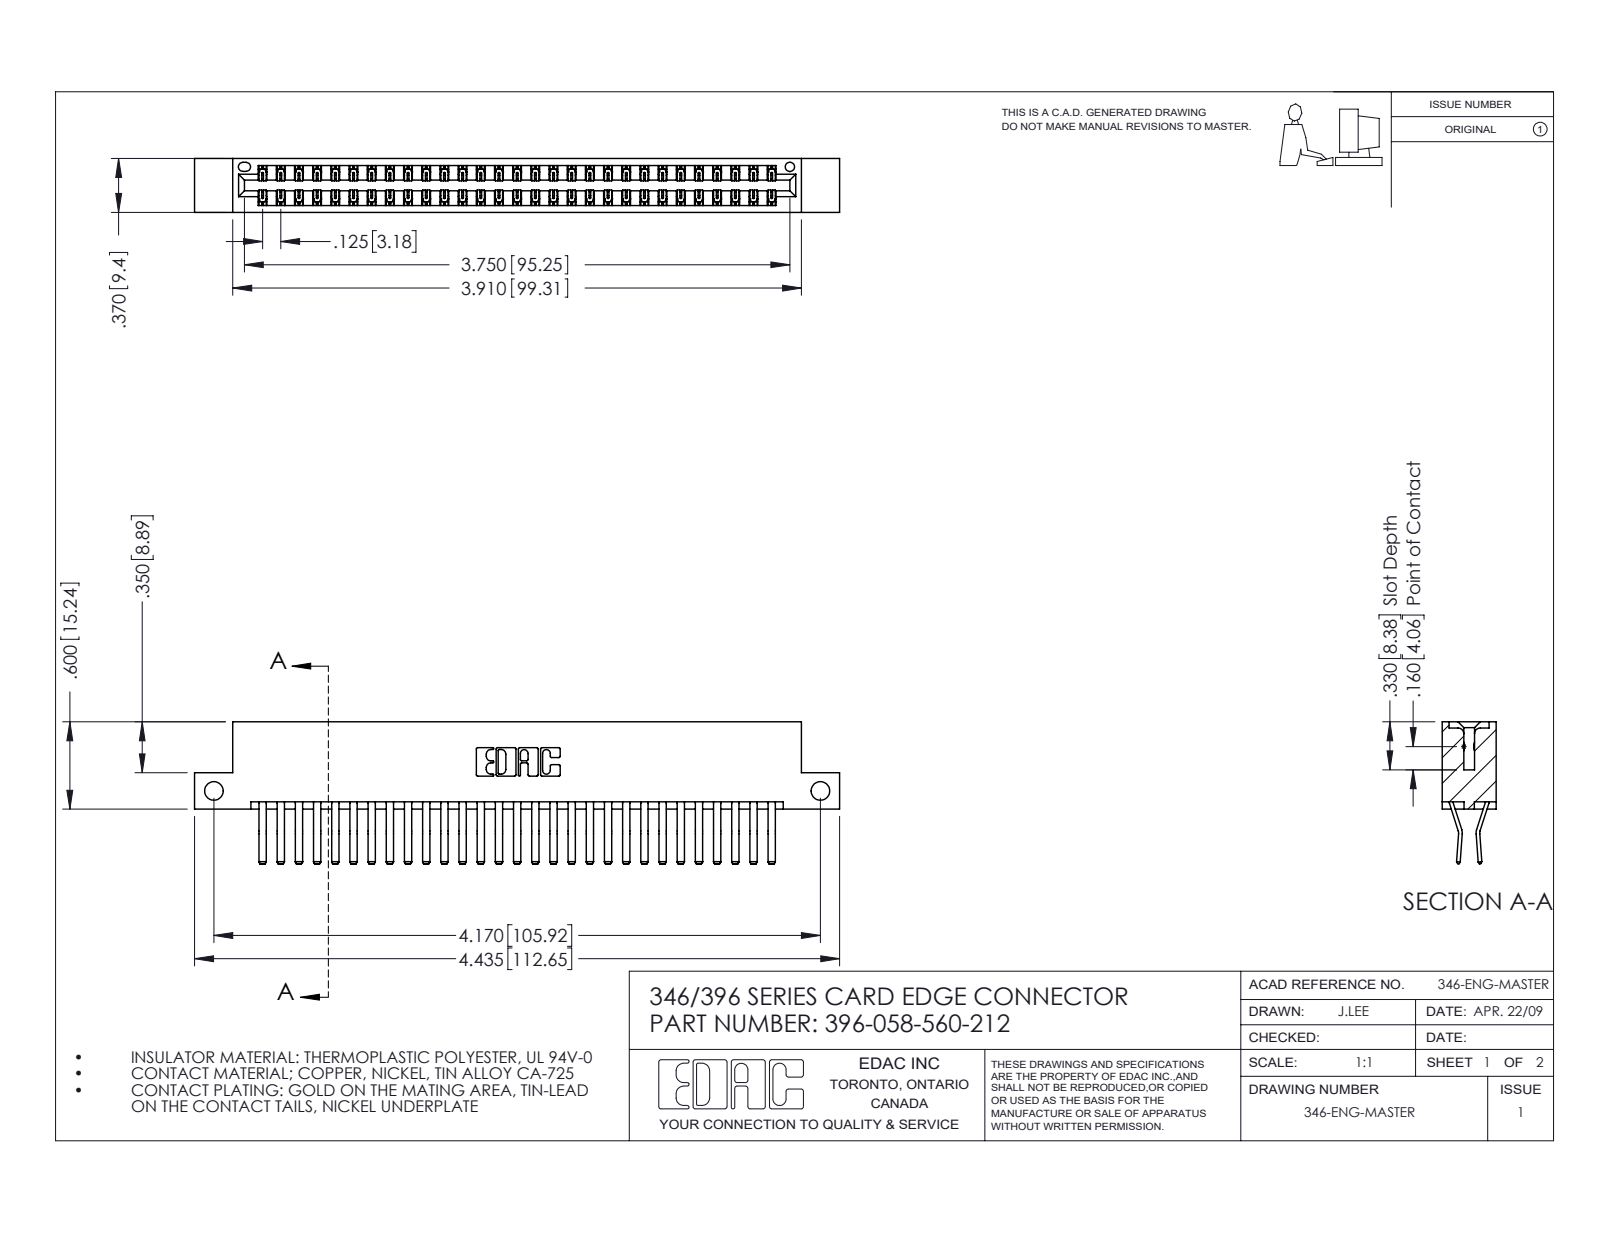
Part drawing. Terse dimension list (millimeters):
name: 396-058-560-212; 346 Part_Flush Mounting Lugs - Side Mount; 345-292-001_560 Tail
written by: SolidWorks 2016 (CONFIG_CONTROL_DESIGN)
unit: mm
bodies: 59 solids, 3254 faces (2106 planar, 1148 cylindrical, 0 other)
size: 112.6 × 24.8 × 9.4
volume: 11 200 mm³; area: 16 040 mm²
holes: 2× ⌀3.3, 1× ⌀1.6
rounds: 87× R0.2, 22× R0.3, 6× R0.2, 6× R0.8, 3× R0.7, 2× R0.3, 2× R0.4, 2× R0.6
face distances: 1.2, 8.2, 9.4, 6.4, 0.6, 1.8, 7.6, 7, 3.8, 5.6
hole spacings: 105.9
